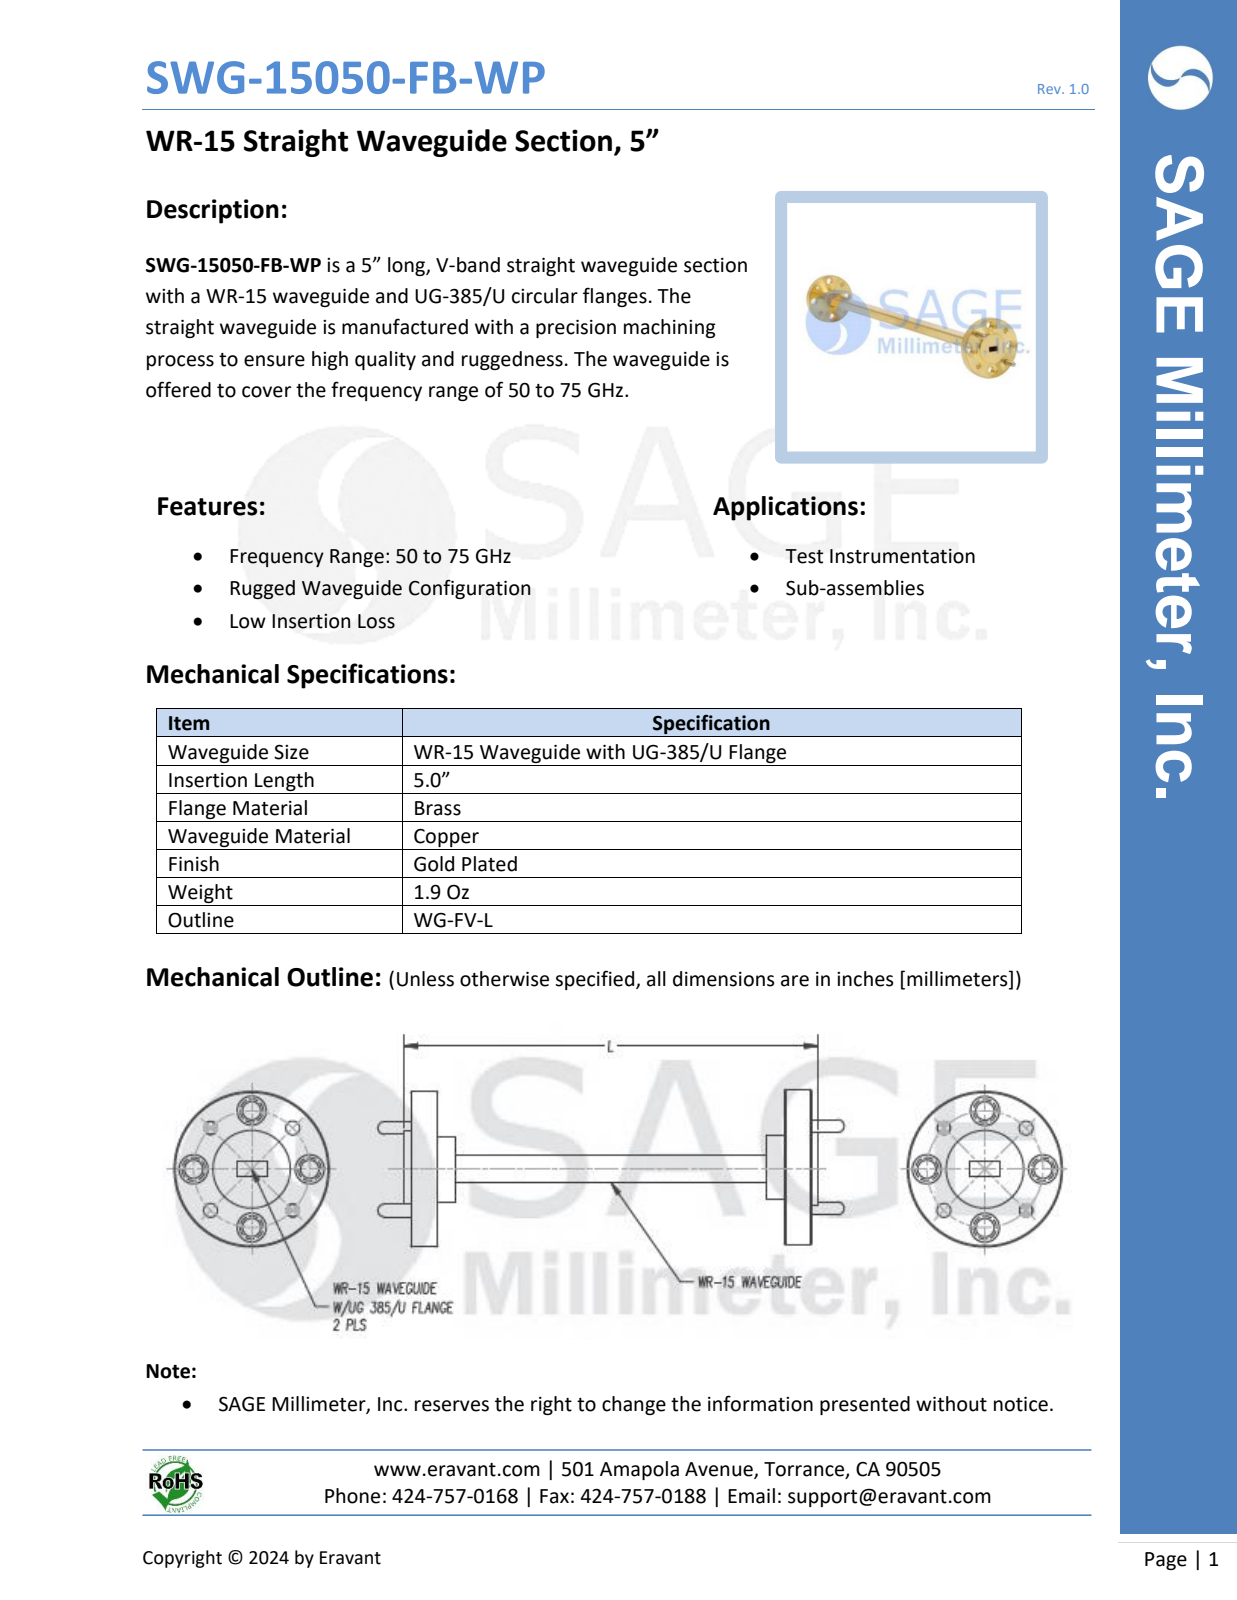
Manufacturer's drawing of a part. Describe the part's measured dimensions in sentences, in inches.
The part is named "SWG-15050-FB". Its 3-D file was written by "SolidWorks 2016 (AUTOMOTIVE_DESIGN)". It is 5 solids with 146 faces: 38 planar, 68 cylindrical and 40 other. Overall it measures 5.305 by 0.75 by 0.75 inches. Its volume is 0.29 cubic inches and its surface area 6.601 square inches. Round holes: 4 of diameter 0.061, 4 of diameter 0.067, 4 of diameter 0.089, 4 of diameter 0.14. Round bosses or shafts: 4 of diameter 0.063, 1 of diameter 0.75, 1 of diameter 0.375, 1 of diameter 0.36. The main face-to-face distances are 0.154, 0.228, 0.13, 4.81, 4.68, 4.94, 0.03, 0.16, 4.84, 4.97. The hole center spacings are 0.215, 0.398, 0.519, 0.562.
